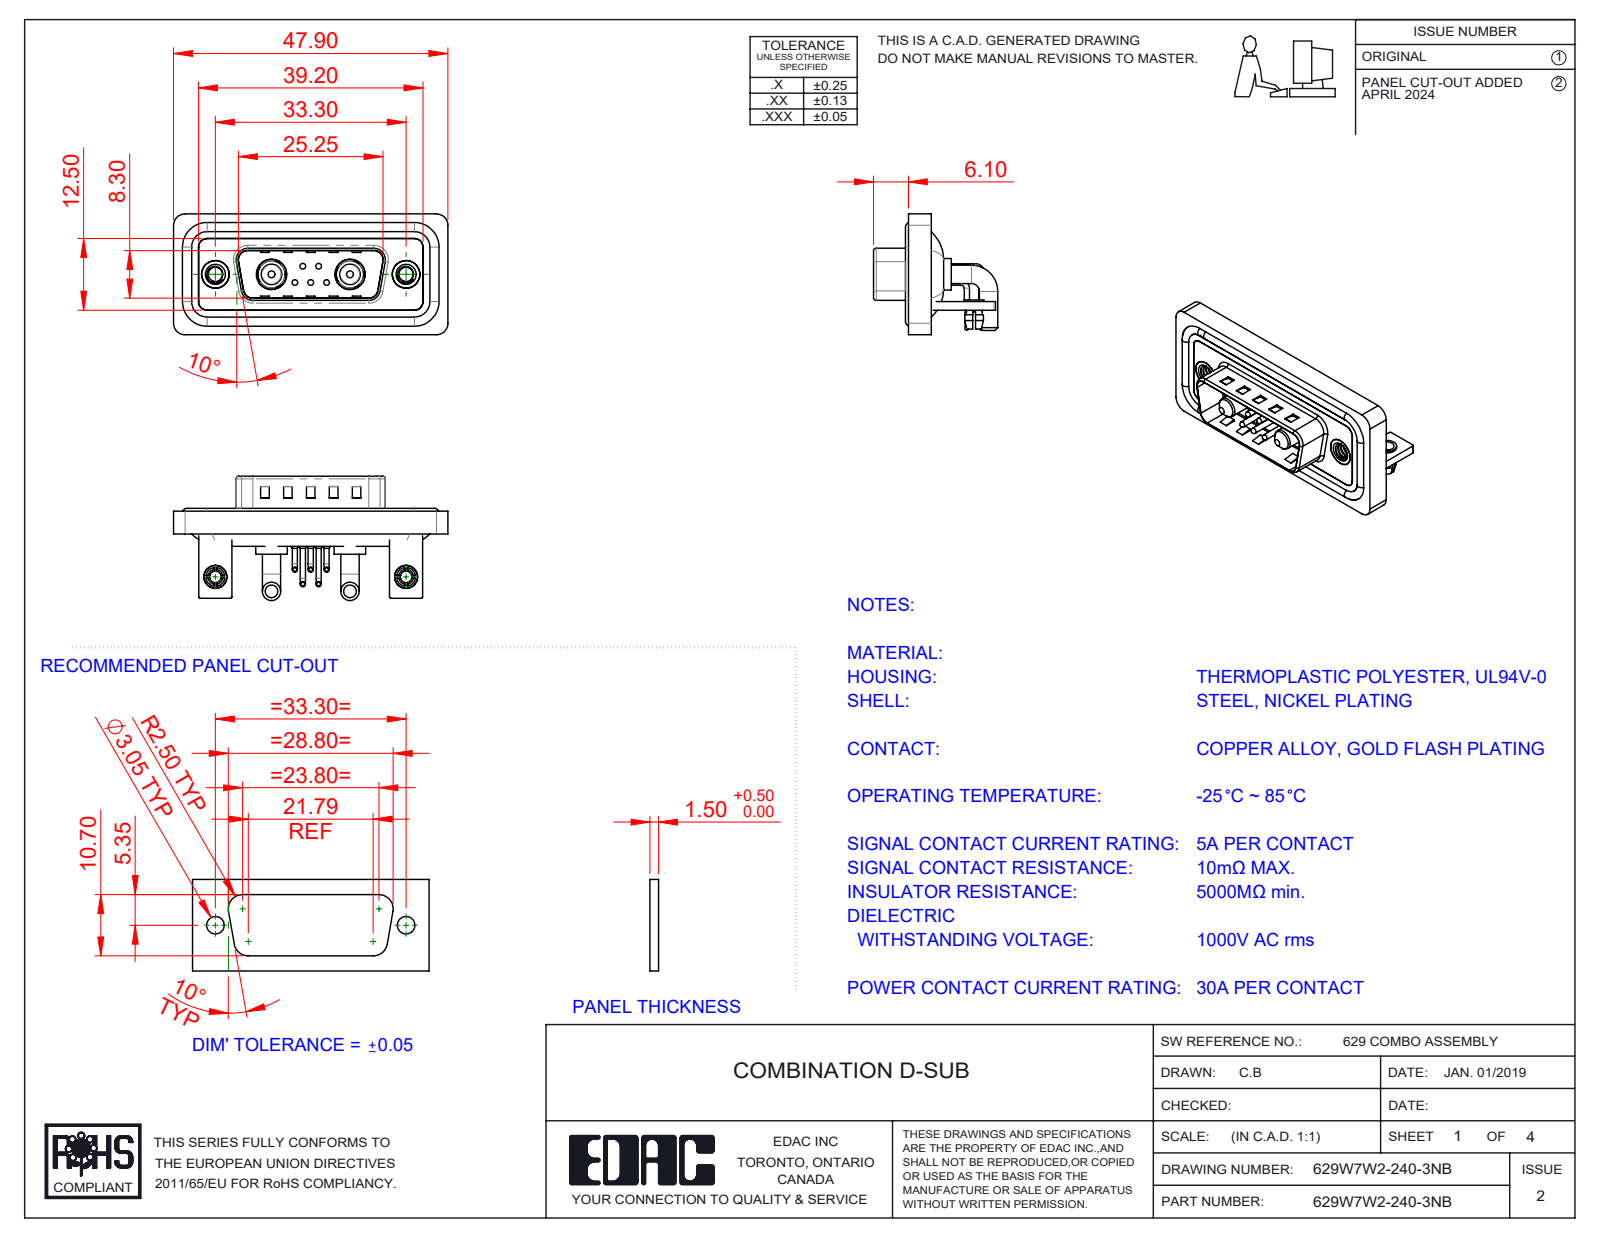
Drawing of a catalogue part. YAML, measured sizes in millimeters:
part_name: "629Combo Housing_7W2; 629Combo Waterproof Housing_15 Contacts; 629Combo Threaded Rivet_B; 629W7W2-140-3NB (+7 more)"
step_written_by: "SolidWorks 2023 (CONFIG_CONTROL_DESIGN)"
units: millimeters
bodies: {solids: 20, faces: 1213, planar: 585, cylindrical: 456, other: 172}
overall_size: [47.9, 21.7, 21.1]
volume: 6045
surface_area: 9976
round_holes:
  - {diameter: 2, count: 7}
  - {diameter: 0.75, count: 5}
  - {diameter: 1.6, count: 5}
  - {diameter: 2.5, count: 4}
  - {diameter: 3.2, count: 2}
  - {diameter: 4, count: 2}
  - {diameter: 4.8, count: 2}
  - {diameter: 4.85, count: 2}
  - {diameter: 5, count: 2}
  - {diameter: 5.3, count: 2}
round_bosses_or_shafts:
  - {diameter: 0.9, count: 10}
  - {diameter: 1.5, count: 5}
  - {diameter: 1, count: 5}
  - {diameter: 0.65, count: 5}
  - {diameter: 3.2, count: 4}
  - {diameter: 1.6, count: 4}
  - {diameter: 5.5, count: 2}
  - {diameter: 5.2, count: 2}
partial_cylinders:
  - {radius: 2, count: 21}
  - {radius: 1.5, count: 18}
  - {radius: 0.25, count: 16}
  - {radius: 0.5, count: 9}
  - {radius: 1.6, count: 8}
  - {radius: 1.01, count: 5}
  - {radius: 0.6, count: 4}
  - {radius: 0.65, count: 4}
face_to_face_distances: [0.4, 1.5, 0.8, 2.9, 2.1, 1.1, 1.6, 1.2, 3.7, 4.5]
hole_center_spacings: [3.16, 2.77, 9.8, 23.5, 33.3, 4.31, 4.33, 5.03]
